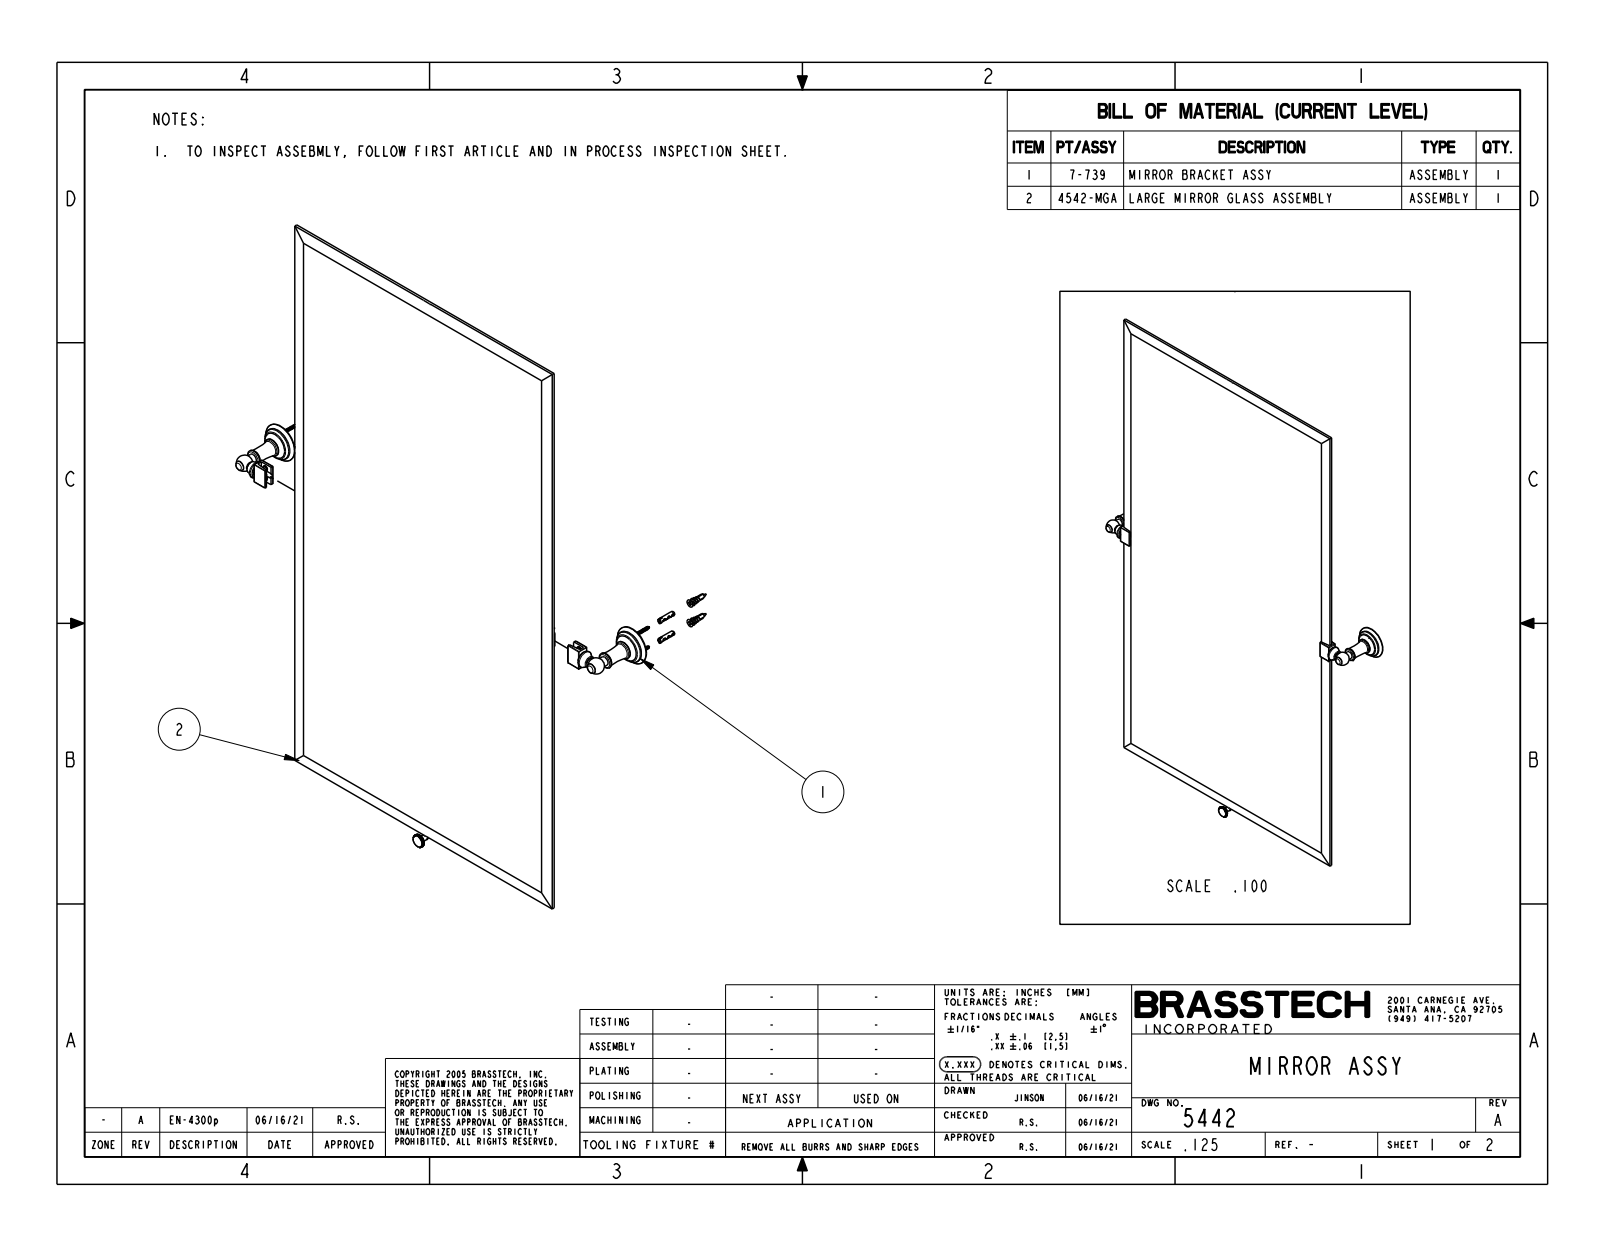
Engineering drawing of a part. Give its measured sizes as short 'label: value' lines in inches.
name: 5442
written by: CREO PARAMETRIC BY PTC INC, 2018400 (CONFIG_CONTROL_DESIGN)
unit: in
bodies: 1 solid, 614 faces (252 planar, 92 cylindrical, 270 other)
size: 36.585 × 24.527 × 3.358
volume: 175.2 in³; area: 1 527 in²
holes: 1× ⌀0.925
bosses: 2× ⌀0.9, 2× ⌀0.56, 2× ⌀0.517, 1× ⌀0.625, 1× ⌀0.46, 1× ⌀0.315
rounds: 24× R0.01, 20× R0.03, 8× R0.039, 2× R0.022
face distances: 0.236, 0.039, 0.275, 2.691, 2.73, 2.967, 1.239, 17.361, 17.4, 18.6
